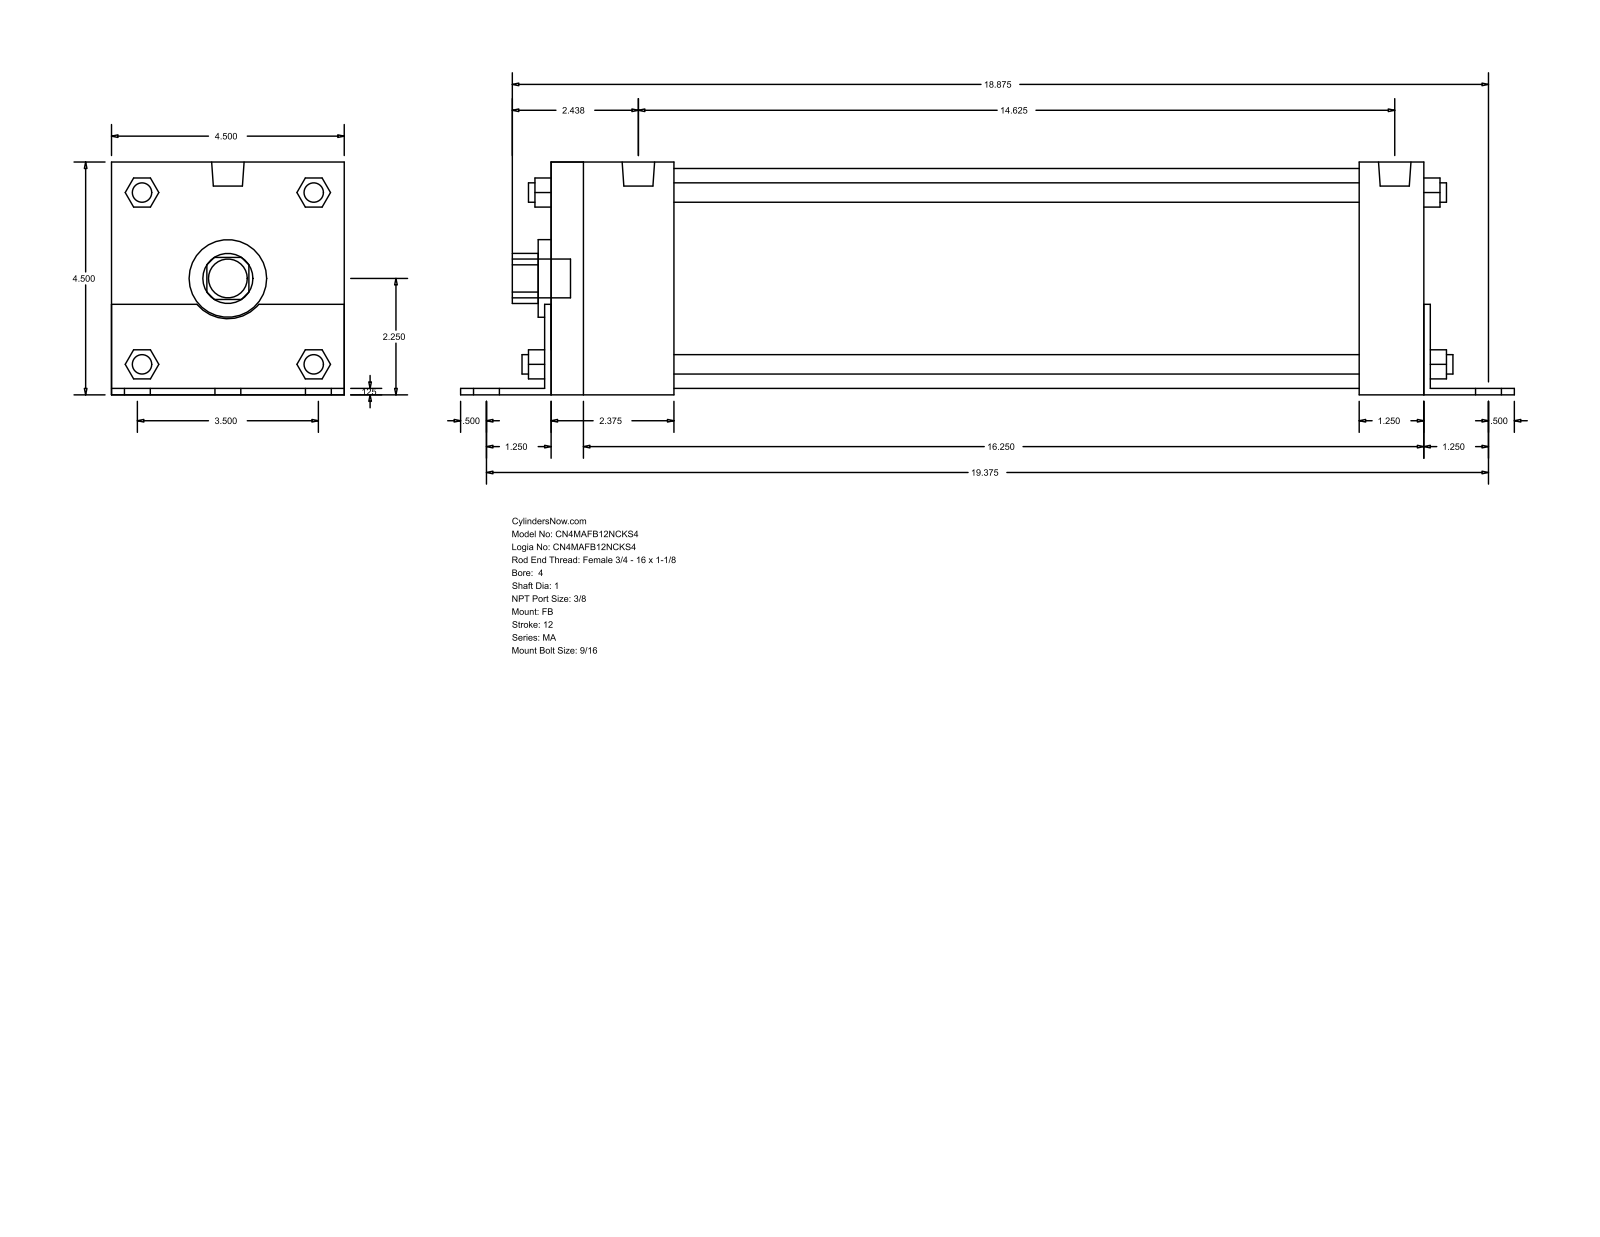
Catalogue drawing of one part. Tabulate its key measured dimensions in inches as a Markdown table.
| quantity | value |
| --- | --- |
| part name | MA_FB__0400_1 |
| STEP written by | GSSL Pune (CONFIG_CONTROL_DESIGN) |
| units | inches |
| bodies | 0 solids, 140 faces (105 planar, 35 cylindrical, 0 other) |
| overall size | 20.375 × 4.502 × 4.5 |
| round holes (diameter × count) | 1 × 1, 1.5 × 1, 4.25 × 1 |
| round bosses / shafts (diameter × count) | 0.563 × 6, 0.437 × 4, 0.375 × 4, 0.627 × 2, 0.75 × 1 |
| partial cylindrical surfaces (radius × count) | 0.484 × 1, 0.78 × 1 |
| main face-to-face distances | 4.5, 0.125, 4.502, 17, 0.123, 4.377, 16.875, 17.125, 15.75, 15.625 |
